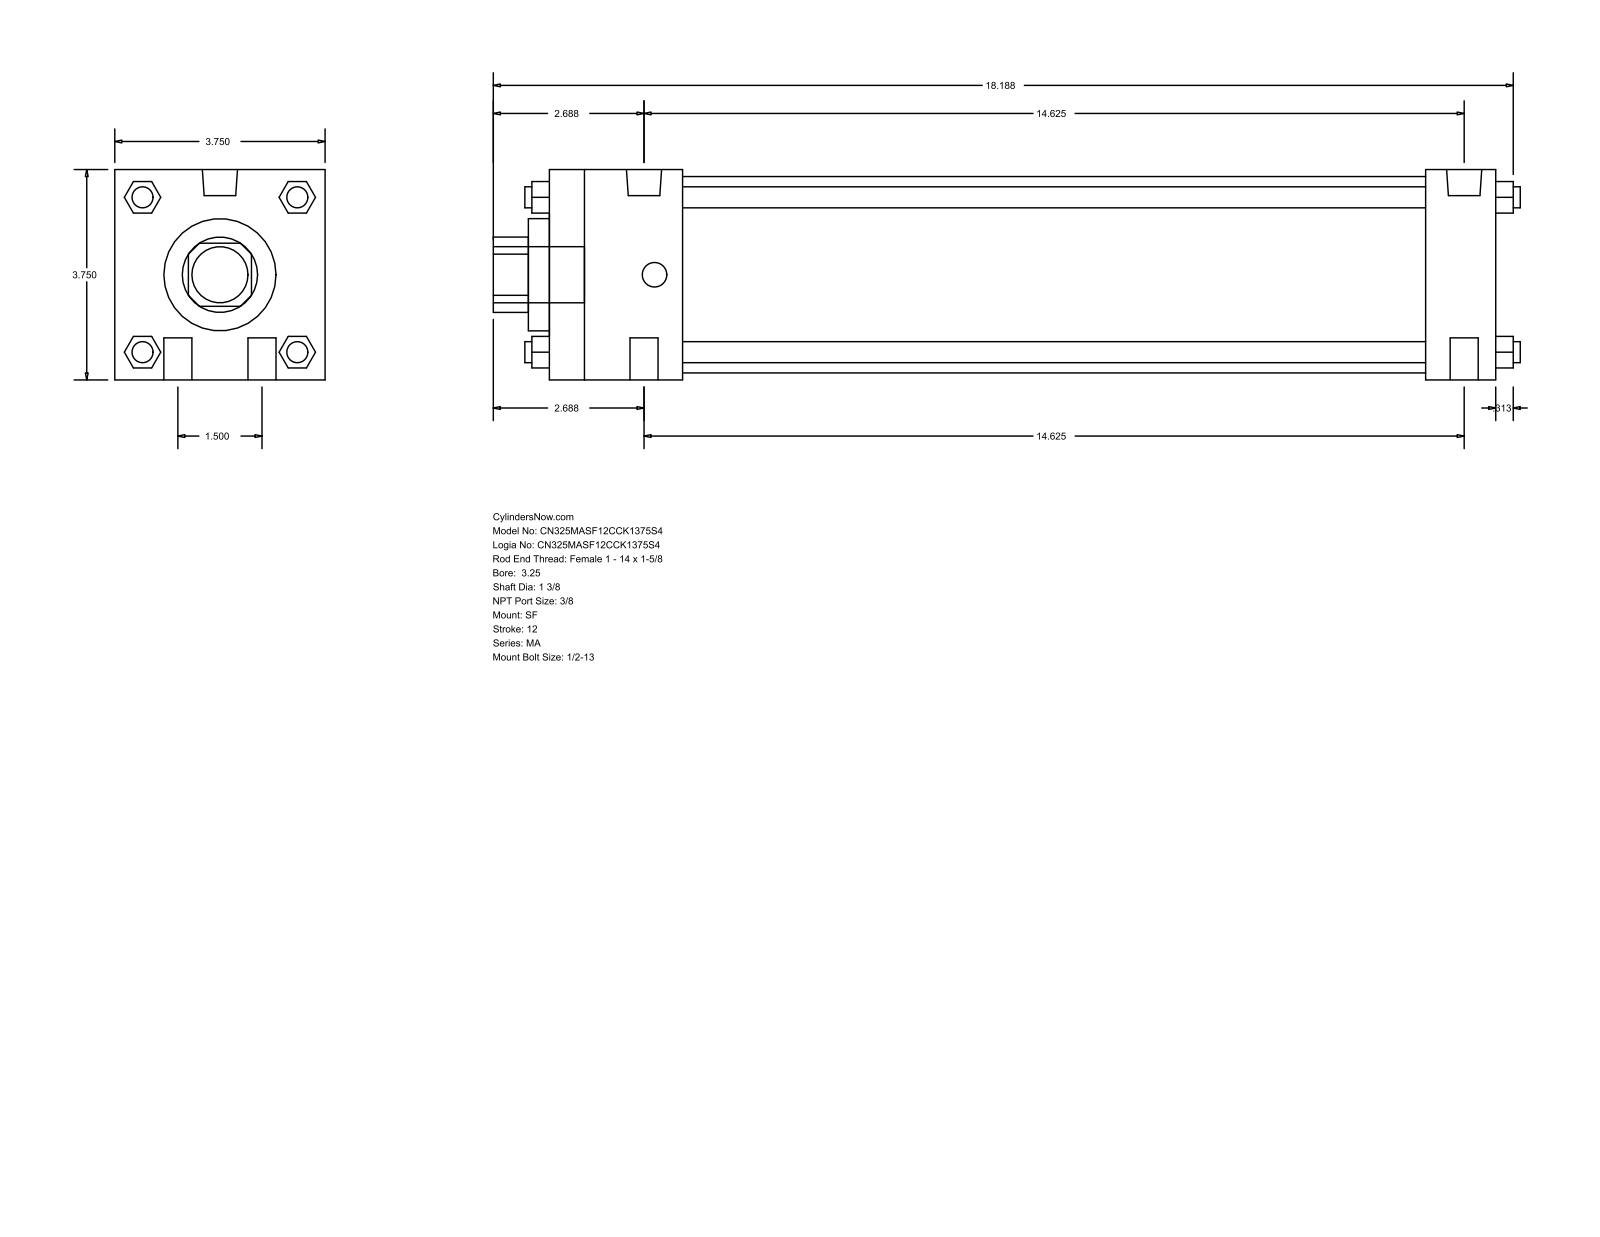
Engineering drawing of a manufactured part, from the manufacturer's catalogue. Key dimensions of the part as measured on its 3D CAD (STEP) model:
Part name (STEP PRODUCT): MA_SF__0325_1.375
STEP written by: GSSL Pune (CONFIG_CONTROL_DESIGN)
Units: millimetres
Bodies: 0 solids, 124 faces (94 planar, 30 cylindrical, 0 other)
Overall size (bounding box): 465.14 × 95.25 × 95.25
Round holes (diameter × count): ⌀34.92 ×1, ⌀50.8 ×1, ⌀88.9 ×1
Round bosses / shafts (diameter × count): ⌀12.7 ×4, ⌀9.53 ×4, ⌀15.93 ×2, ⌀11.11 ×2, ⌀25.4 ×1
Partial cylindrical surfaces — rounded edges, fillets, slot ends (radius × count): R17.06 ×1
Main face-to-face distances: 95.24, 428.62, 396.87, 31.75, 60.32, 336.55, 368.3, 9.52, 69.84, 406.39
